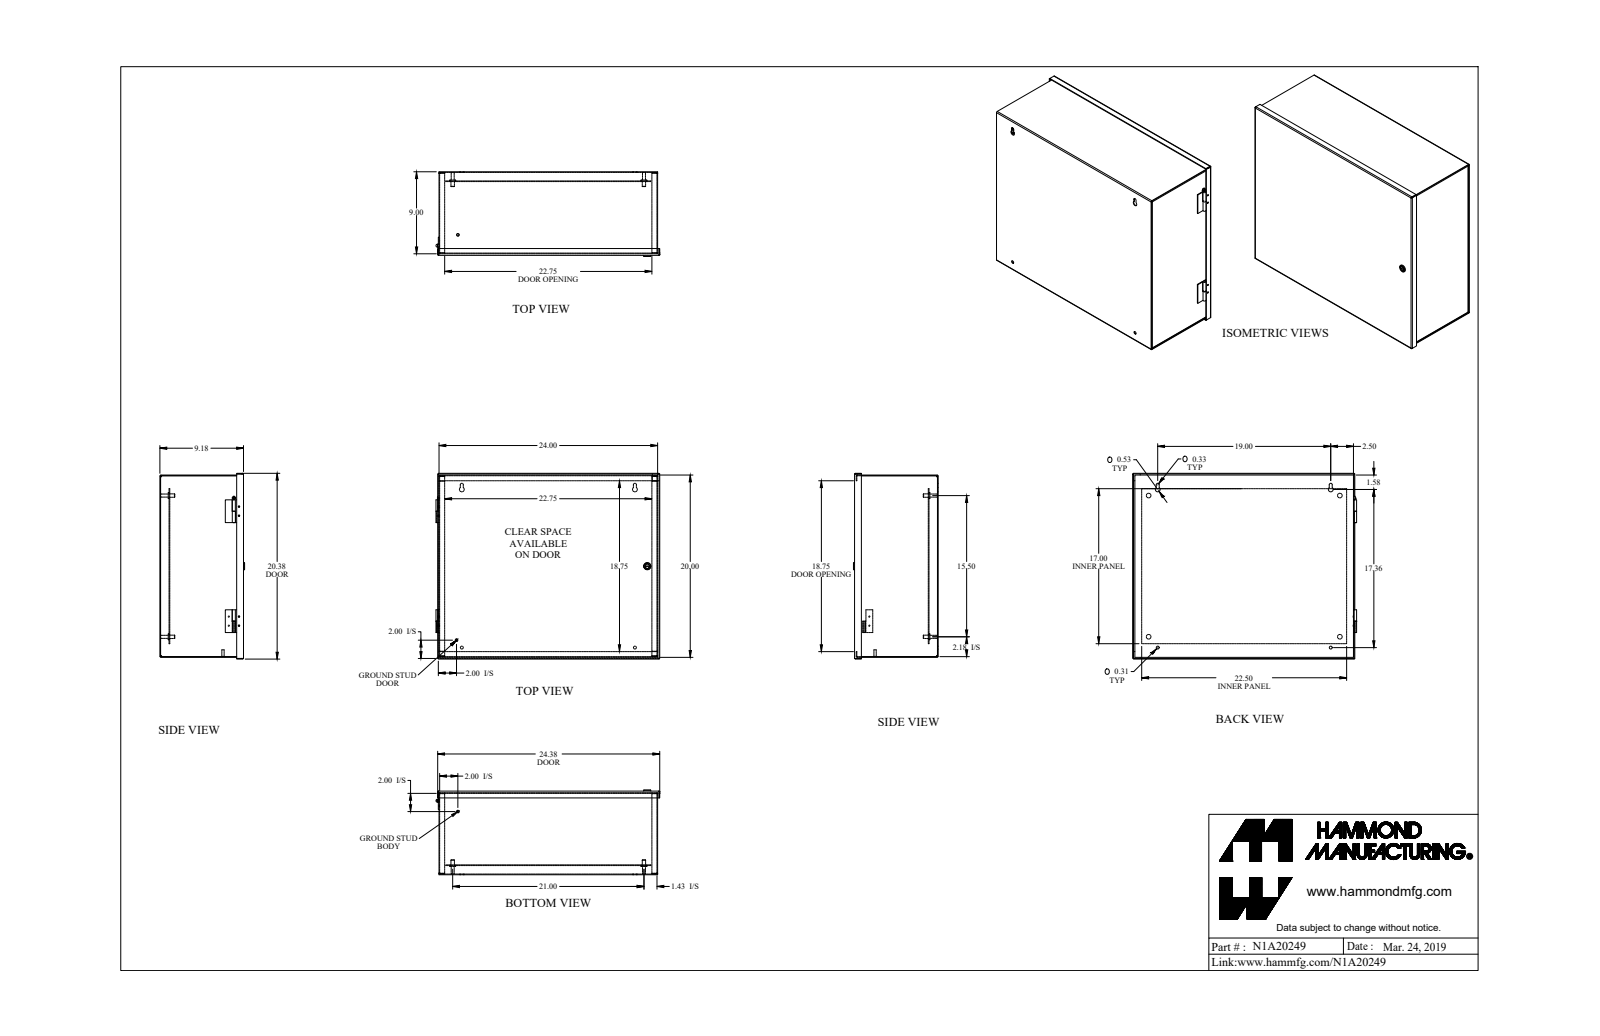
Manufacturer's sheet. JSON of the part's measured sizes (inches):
{"part_name": "N1A20249", "step_written_by": "SolidWorks 2018 (AUTOMOTIVE_DESIGN)", "units": "inches", "bodies": {"solids": 23, "faces": 520, "planar": 294, "cylindrical": 182, "other": 44}, "overall_size": [24.574, 20.384, 9.299], "volume_in3": 166.6, "surface_area_in2": 4642, "round_holes": [[0.14, 8], [0.5, 4], [0.307, 2], [0.312, 2], [0.445, 2], [0.17, 1], [0.187, 1], [0.516, 1]], "round_bosses_or_shafts": [[0.128, 8], [0.375, 5], [0.65, 4], [0.33, 4], [1, 2], [0.281, 2], [0.25, 2], [0.788, 1]], "partial_cylinders_radius": [[0.036, 16], [0.108, 16], [0.06, 2], [0.153, 2], [0.164, 2], [0.266, 2], [0.03, 1], [0.125, 1]], "face_to_face_distances": [0.072, 9.105, 1.009, 8.096, 9.033, 9.177, 19.928, 1.081, 8.024, 0.937], "hole_center_spacings": [1, 1.119, 1.553, 2.031, 7.758, 12.062, 12.062, 12.113]}
